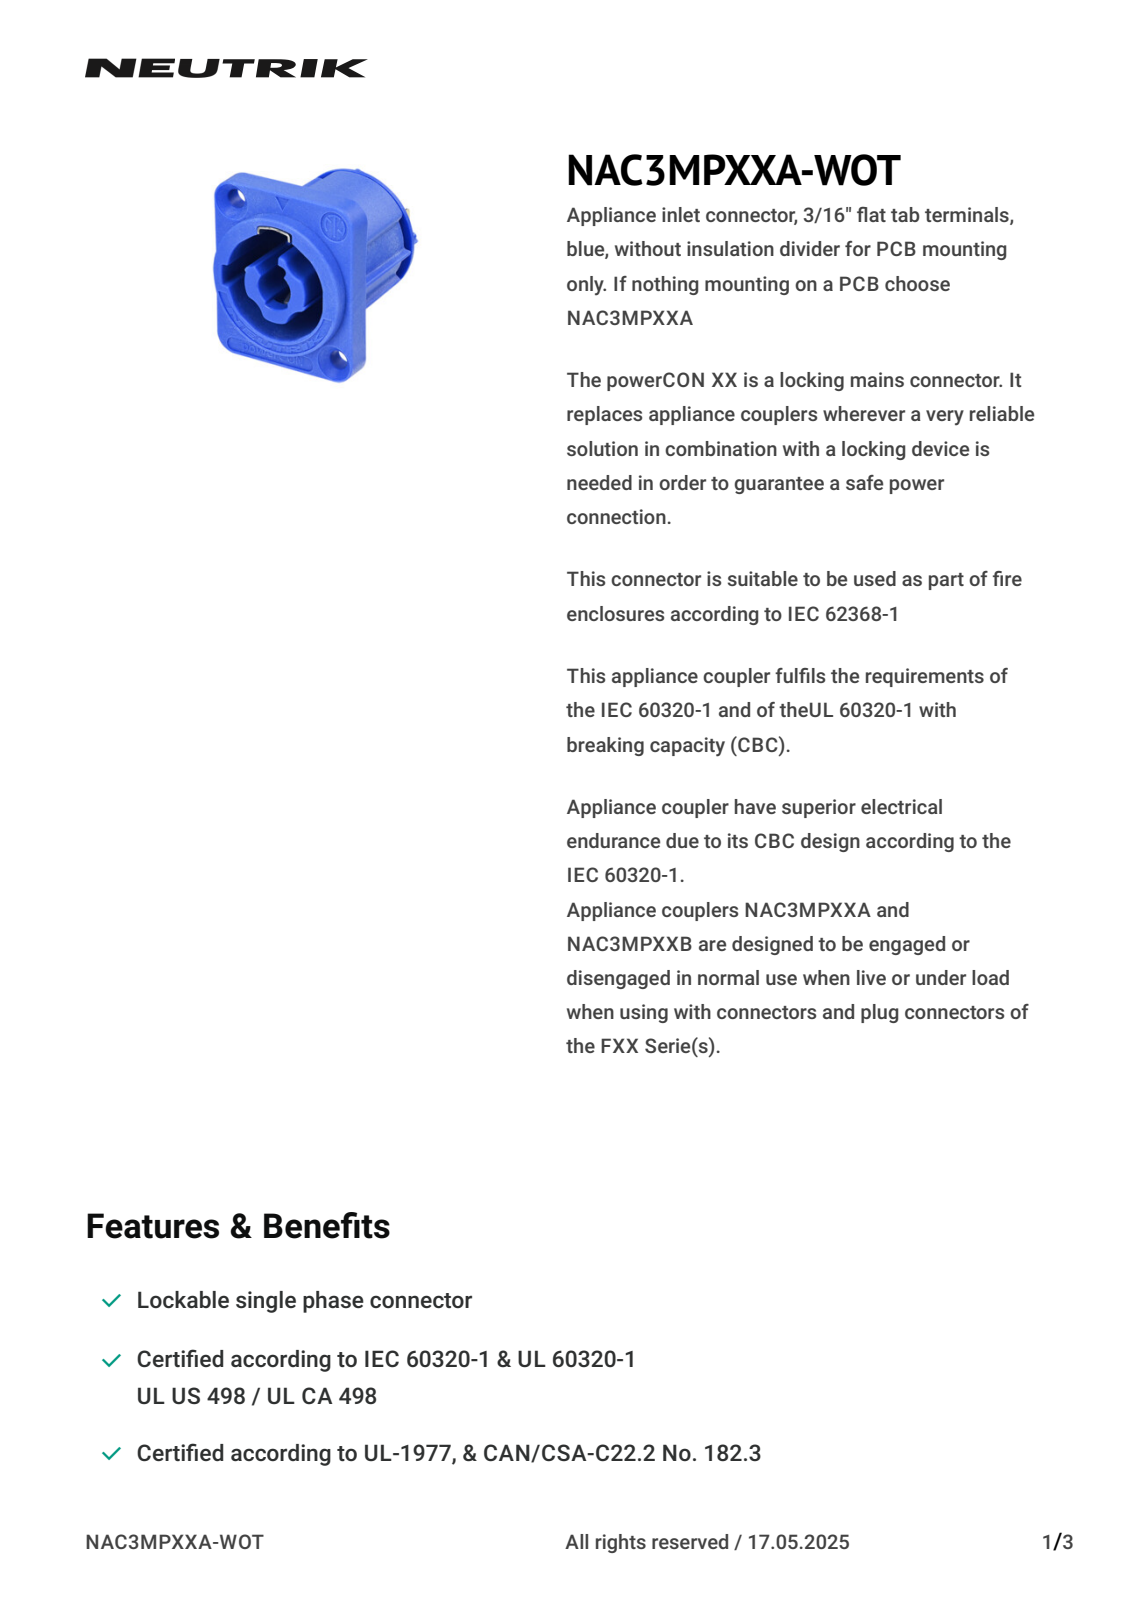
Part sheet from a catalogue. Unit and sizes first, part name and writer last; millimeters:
Units: millimetres
Overall size (bounding box): 34.3 × 30.9 × 25.9
Round holes (diameter × count): ⌀1.4 ×2, ⌀6 ×2, ⌀4.2 ×1, ⌀5 ×1
Round bosses / shafts (diameter × count): ⌀22.5 ×1, ⌀19.6 ×1, ⌀3.65 ×1
Partial cylindrical surfaces — rounded edges, fillets, slot ends (radius × count): R0.2 ×54, R0.5 ×21, R0.3 ×20, R0.25 ×11, R0.21 ×9, R0.14 ×7, R0.28 ×3, R0.15 ×2
Main face-to-face distances: 4.55, 2.5, 23.6, 23.55, 4.5, 19.05, 2.55, 26.1, 7.05, 20.45
Hole centre spacings: 20.83, 10.96, 19, 24, 30.61
Volume: 10 510 mm³ · Surface area: 5 706 mm²
Bodies: 1 solid, 1213 faces (365 planar, 185 cylindrical, 663 other)
Part name (STEP PRODUCT): NAC3MPXXA-WOT
STEP written by: CREO PARAMETRIC BY PTC INC, 2019080 (CONFIG_CONTROL_DESIGN)
